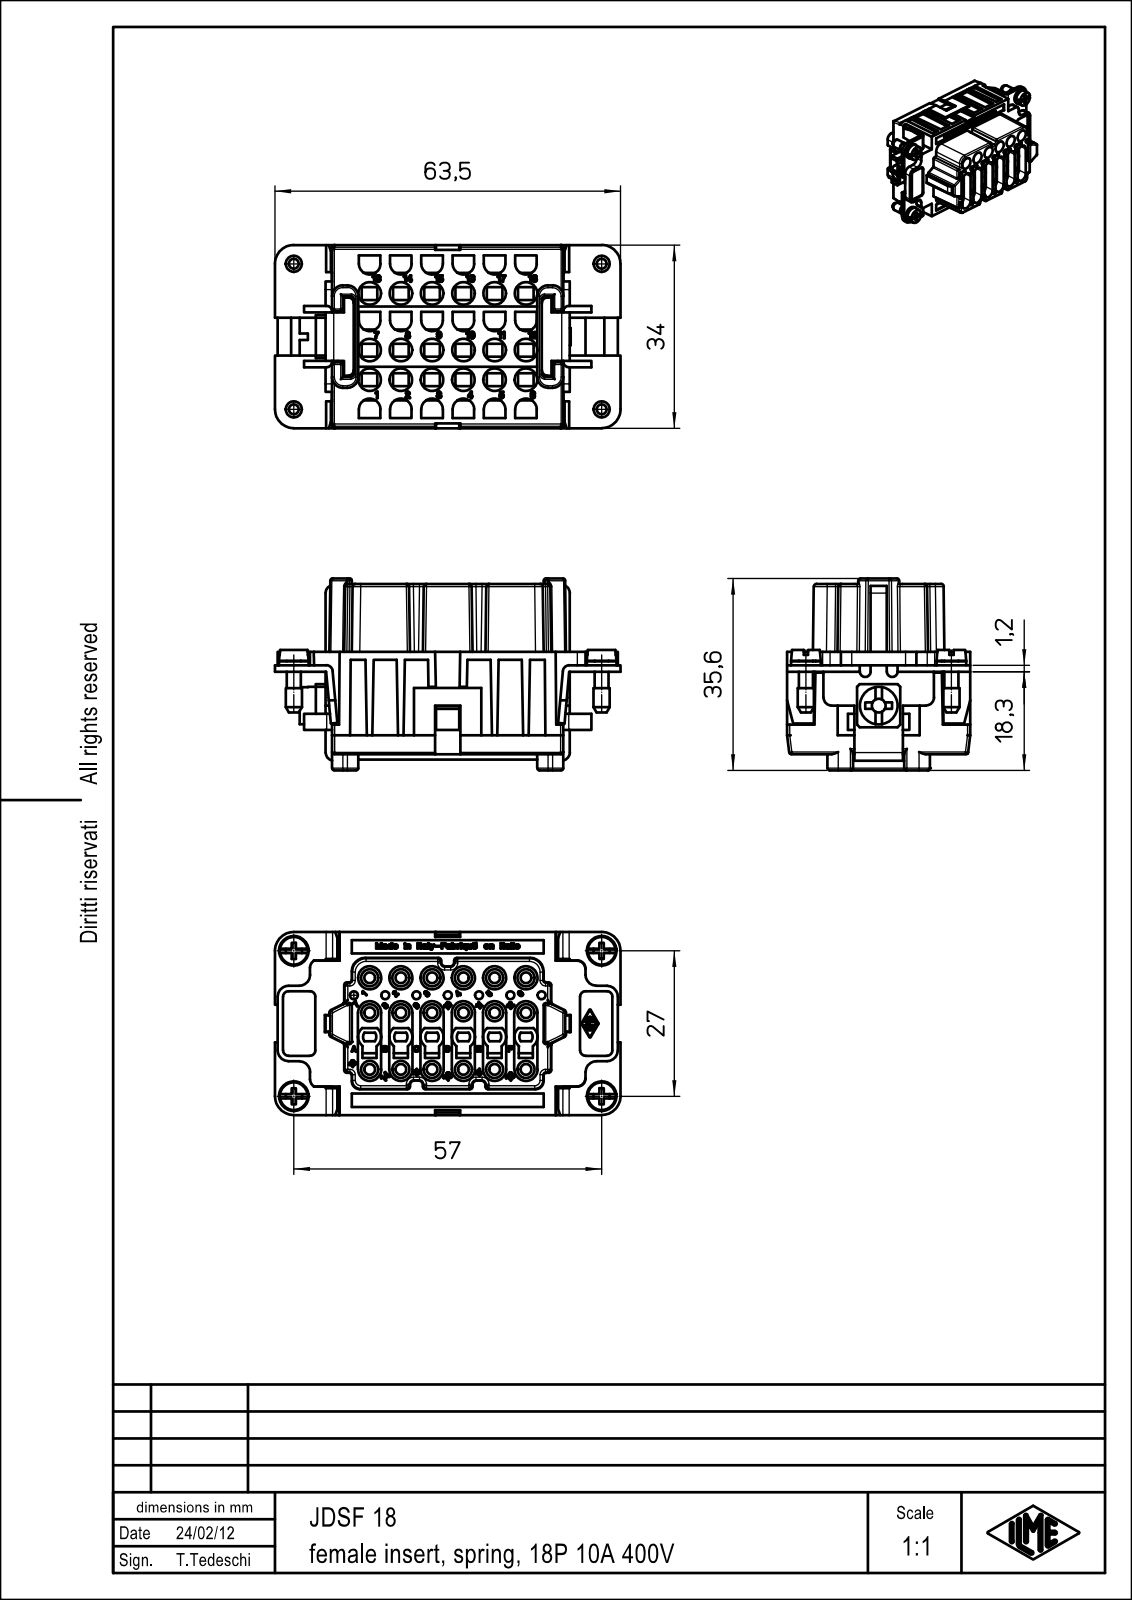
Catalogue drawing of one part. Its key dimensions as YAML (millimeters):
part_name: "JDSF_18"
step_written_by: "Creo Elements/Direct Modeling 18.0B 02-Dec-2011 (C) Parametric Technology GmbH (AUTOMOTIVE_DESIGN)"
units: millimeters
bodies: {solids: 1, faces: 4592, planar: 3953, cylindrical: 406, other: 233}
overall_size: [64.1, 35.6, 34]
volume: 35507
surface_area: 18727
round_holes:
  - {diameter: 2, count: 18}
  - {diameter: 4.2, count: 18}
  - {diameter: 1.5, count: 7}
  - {diameter: 4.3, count: 6}
  - {diameter: 2.58, count: 1}
  - {diameter: 3, count: 1}
round_bosses_or_shafts:
  - {diameter: 5.5, count: 4}
  - {diameter: 3, count: 4}
  - {diameter: 2.6, count: 4}
  - {diameter: 7, count: 1}
partial_cylinders:
  - {radius: 0.5, count: 41}
  - {radius: 2, count: 34}
  - {radius: 0.4, count: 25}
  - {radius: 1, count: 20}
  - {radius: 2.15, count: 18}
  - {radius: 1.5, count: 14}
  - {radius: 0.8, count: 6}
  - {radius: 1.25, count: 6}
face_to_face_distances: [1.2, 0.9, 1, 33.1, 11.6, 18.7, 16.3, 2.2, 19, 11.5]
hole_center_spacings: [4.36, 5.8, 9.29, 11.6, 14.86, 17.4, 14.05, 20.56]
